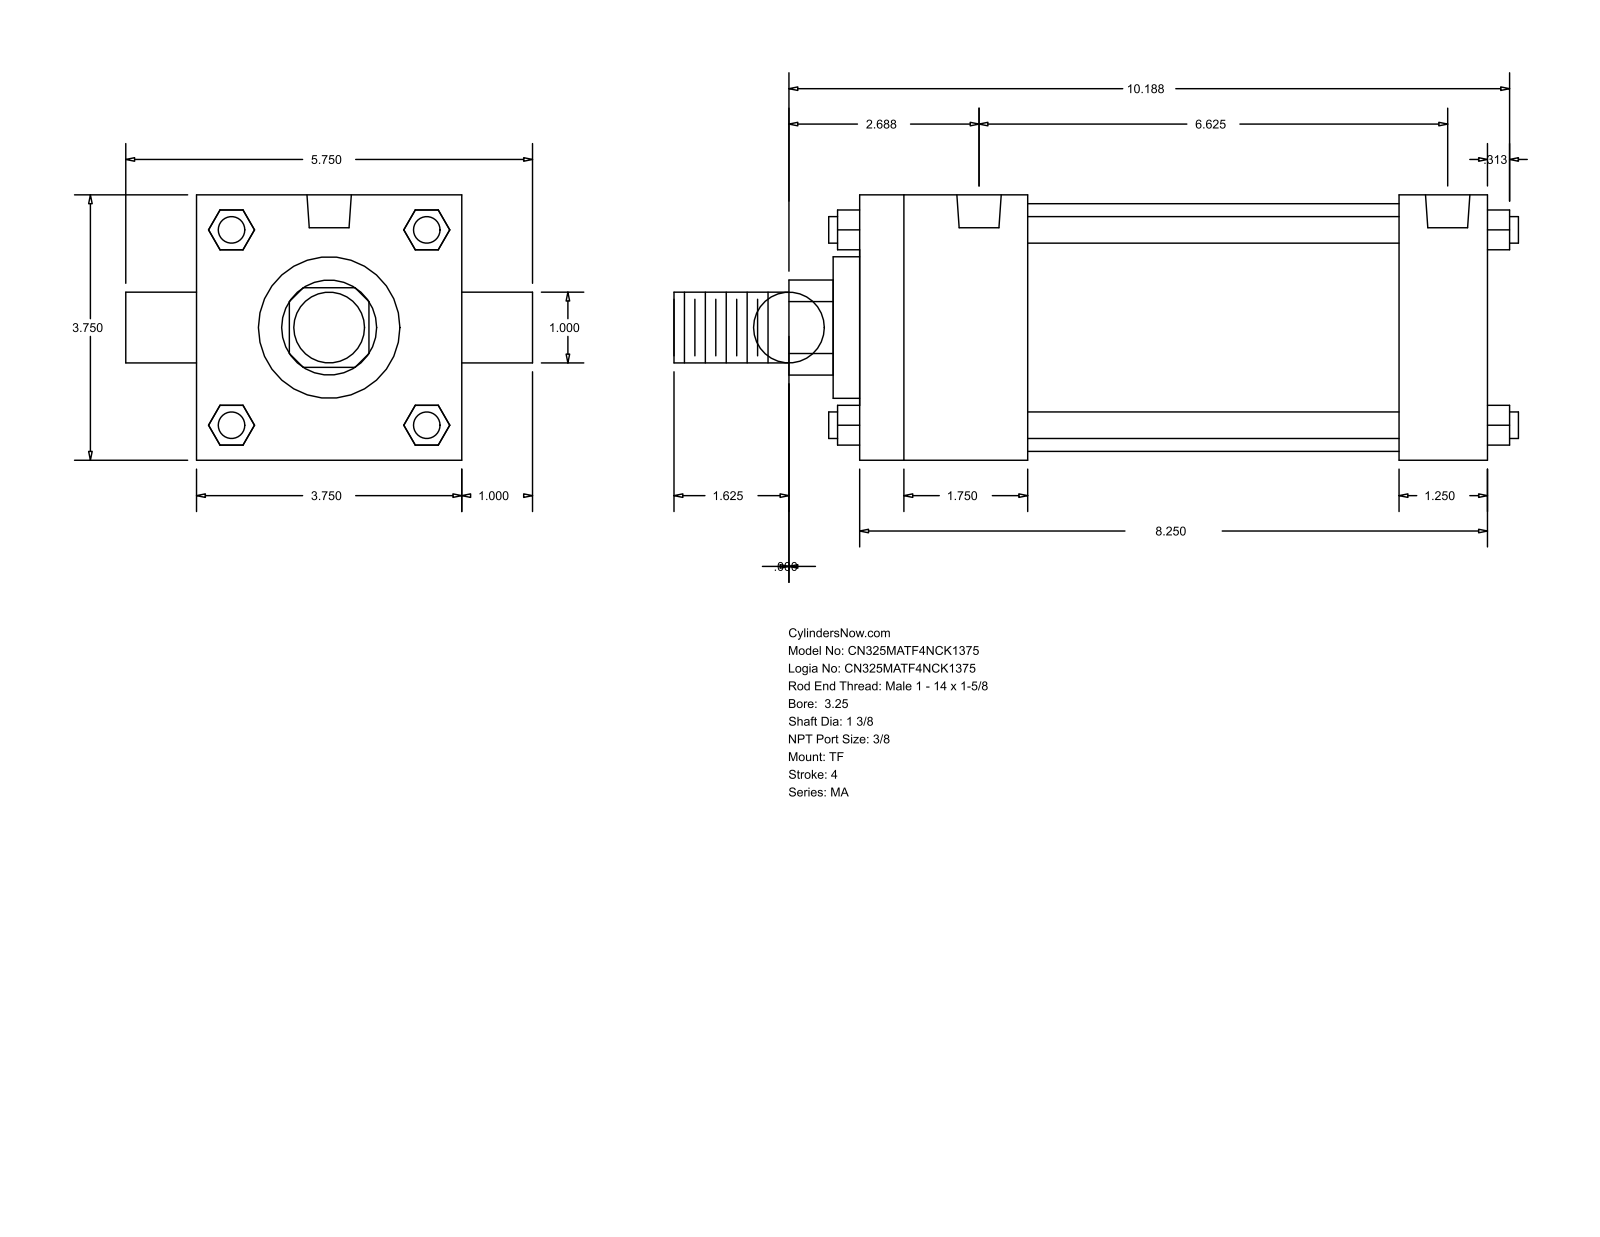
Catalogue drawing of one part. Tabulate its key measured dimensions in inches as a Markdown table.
| quantity | value |
| --- | --- |
| part name | MA_TF__0325_1.375 |
| STEP written by | GSSL Pune (CONFIG_CONTROL_DESIGN) |
| units | inches |
| bodies | 0 solids, 120 faces (92 planar, 28 cylindrical, 0 other) |
| overall size | 11.937 × 5.75 × 3.75 |
| round holes (diameter × count) | 0.437 × 3, 0.627 × 2 |
| round bosses / shafts (diameter × count) | 0.375 × 4, 1 × 2, 3.5 × 1, 2 × 1, 1.375 × 1 |
| partial cylindrical surfaces (radius × count) | 0.672 × 1 |
| main face-to-face distances | 3.75, 8.875, 2.375, 7.625, 5.25, 6.5, 1.25, 0.375, 2.75, 8 |
| hole center spacings | 0.187, 0.188, 6.25, 6.437, 6.438, 6.625 |
